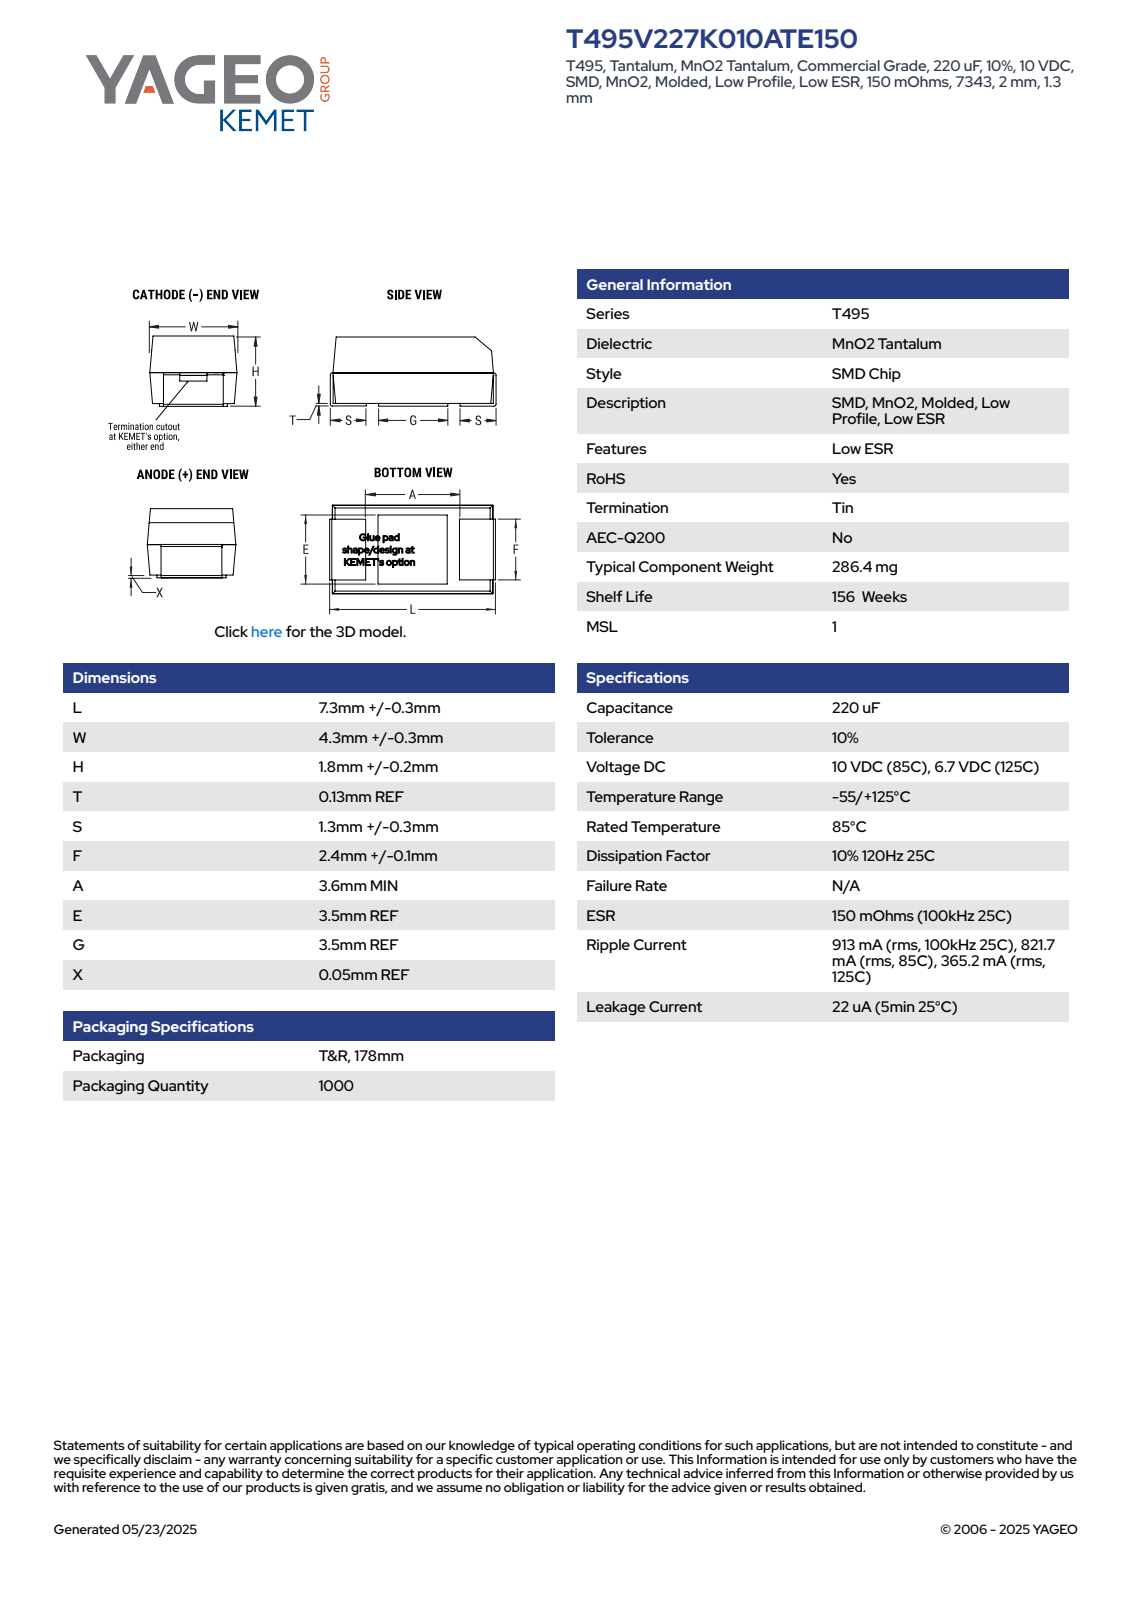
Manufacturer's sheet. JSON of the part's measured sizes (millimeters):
{"part_name": "CTSM_TCM2NBKRP_7343_L7.6W4.6H2T0.13S1.3F2.5A3.6E3.5G3.5X0.05", "step_written_by": "SolidWorks 2020 (AUTOMOTIVE_DESIGN)", "units": "millimeters", "bodies": {"solids": 4, "faces": 94, "planar": 90, "cylindrical": 4, "other": 0}, "overall_size": [7.6, 4.6, 2], "volume_mm3": 61, "surface_area_mm2": 115, "partial_cylinders_radius": [[0.1, 4]], "face_to_face_distances": [2, 1.95, 4.45, 4.44, 7.47, 7.6, 7.34, 1.87, 2.05, 5.55]}
